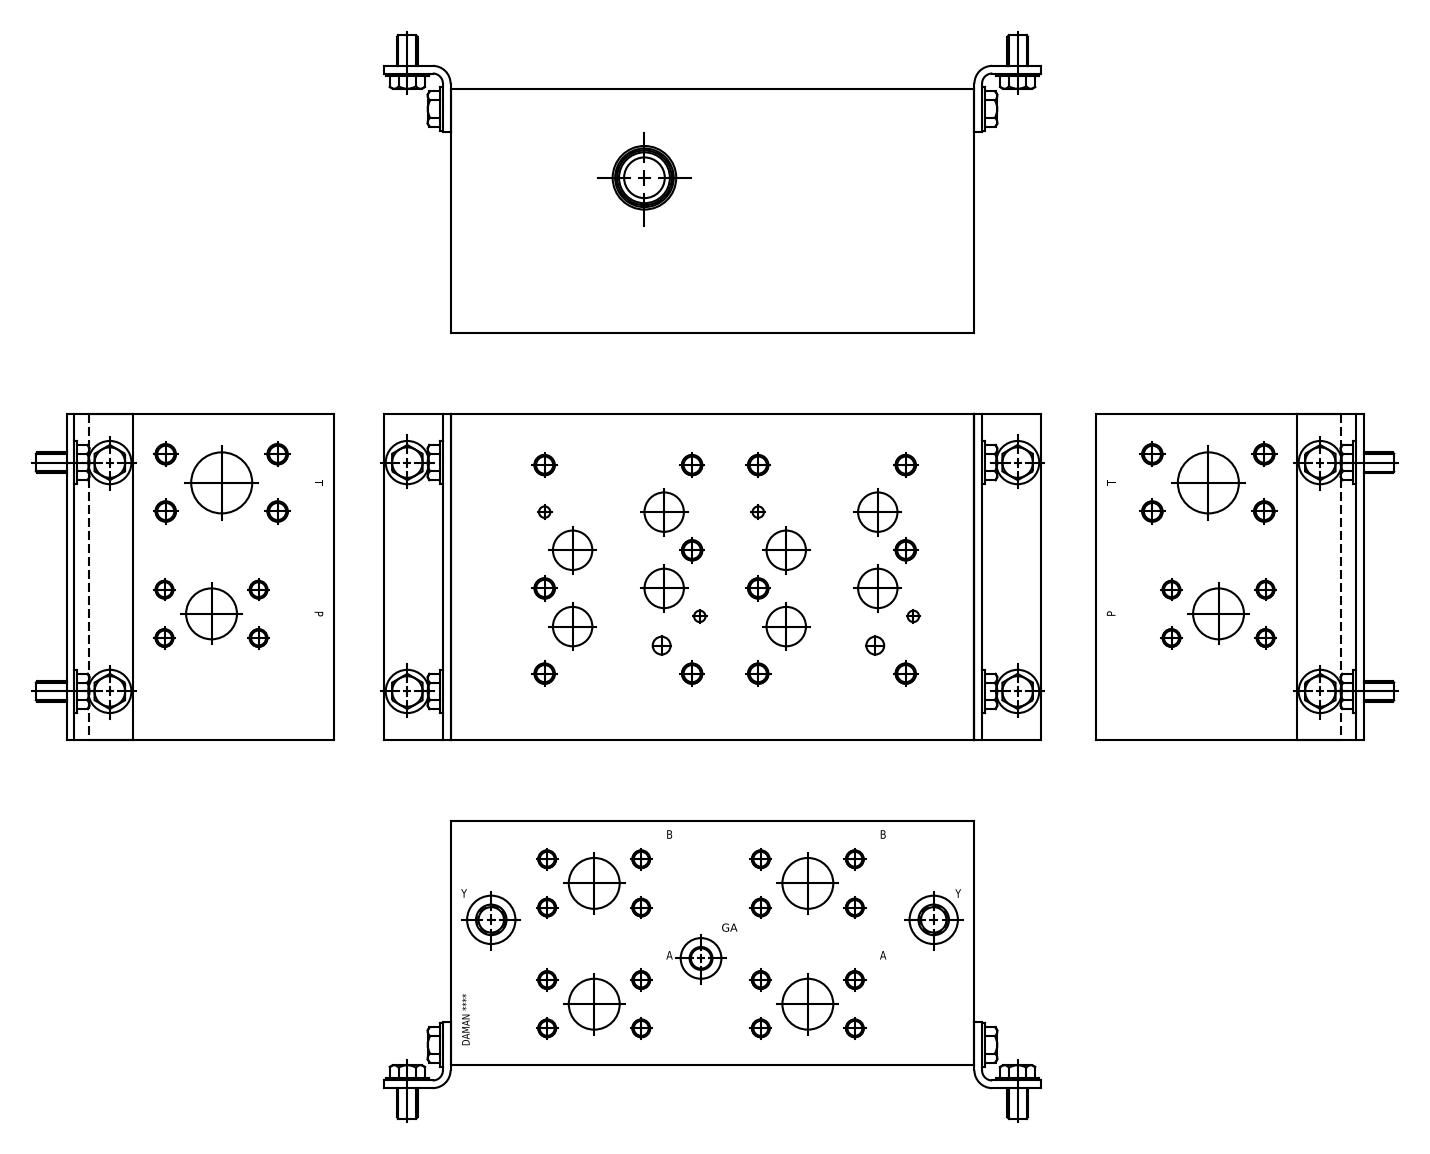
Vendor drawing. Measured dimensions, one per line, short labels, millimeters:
name: Part_AD08HP025F~S_3D
written by: Autodesk Inventor 2021 (AUTOMOTIVE_DESIGN)
unit: mm
bodies: 1 solid, 813 faces (424 planar, 139 cylindrical, 250 other)
size: 327.02 × 203.2 × 152.4
volume: 9 742 000 mm³; area: 379 512 mm²
holes: 25× ⌀11.13, 23× ⌀9.35, 20× ⌀12.7, 18× ⌀10.72, 8× ⌀24.61, 6× ⌀31.75, 4× ⌀7.14, 2× ⌀17.5, 2× ⌀19.05, 2× ⌀19.25, 2× ⌀30.63, 1× ⌀12.29
face distances: 152.4, 203.2, 327.02, 0.79, 202.41, 30.23, 28.45, 27.66, 174.75, 122.17
hole spacings: 33.01, 133.35, 30.18, 58.72, 66.02, 75.41, 153.2, 95.14
